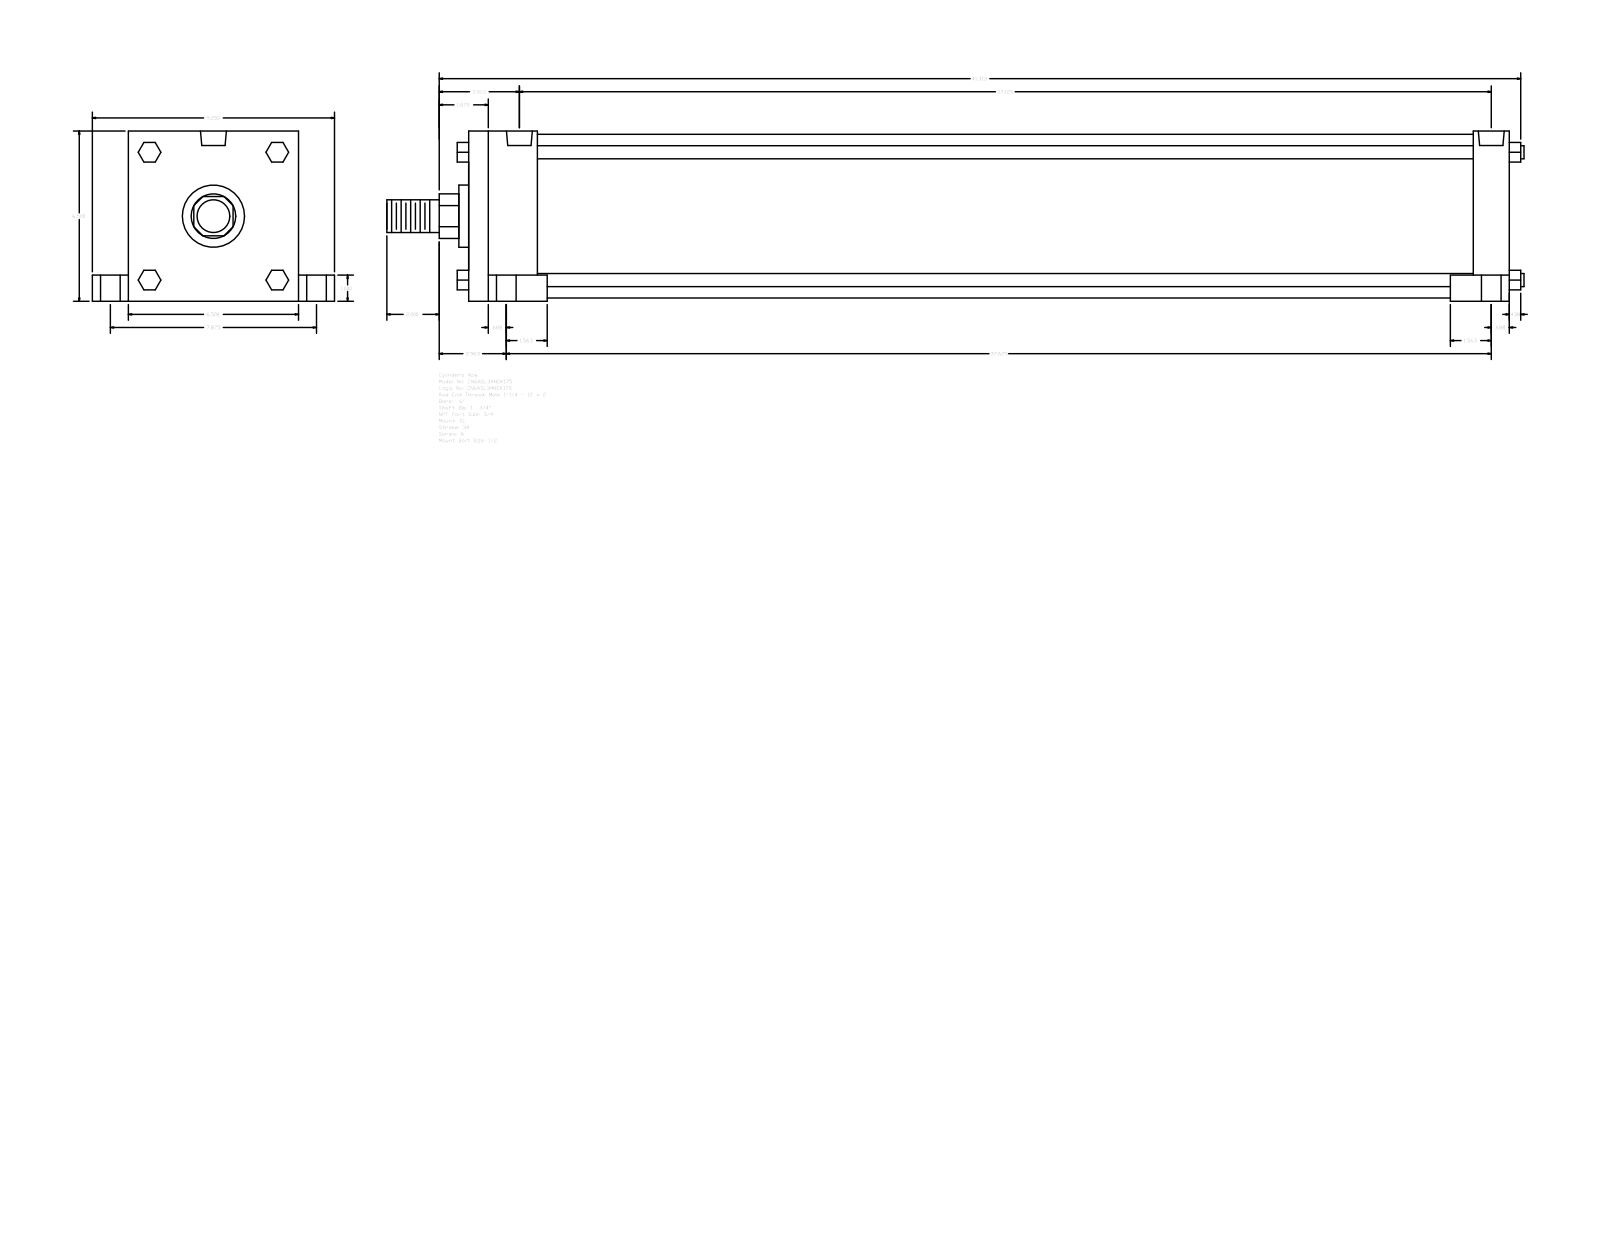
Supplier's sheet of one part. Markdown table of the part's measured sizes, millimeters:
| quantity | value |
| --- | --- |
| part name | A_SL__0600_1.75 |
| STEP written by | GSSL Pune (CONFIG_CONTROL_DESIGN) |
| units | millimeters |
| bodies | 0 solids, 150 faces (114 planar, 36 cylindrical, 0 other) |
| overall size | 1103.31 × 234.95 × 165.1 |
| round holes (diameter × count) | 15.08 × 4, 19.05 × 4, 25.4 × 4, 25.12 × 2 |
| round bosses / shafts (diameter × count) | 12.7 × 4, 158.75 × 1, 60.33 × 1, 44.45 × 1, 31.75 × 1 |
| partial cylindrical surfaces (radius × count) | 21.63 × 1 |
| main face-to-face distances | 165.1, 1009.65, 34.92, 66.68, 942.97, 974.73, 908.05, 25.4, 139.7, 200.02 |
| hole center spacings | 5.56, 100.01, 100.16, 100.81, 101.66, 200.02, 931.85, 937.41 |
